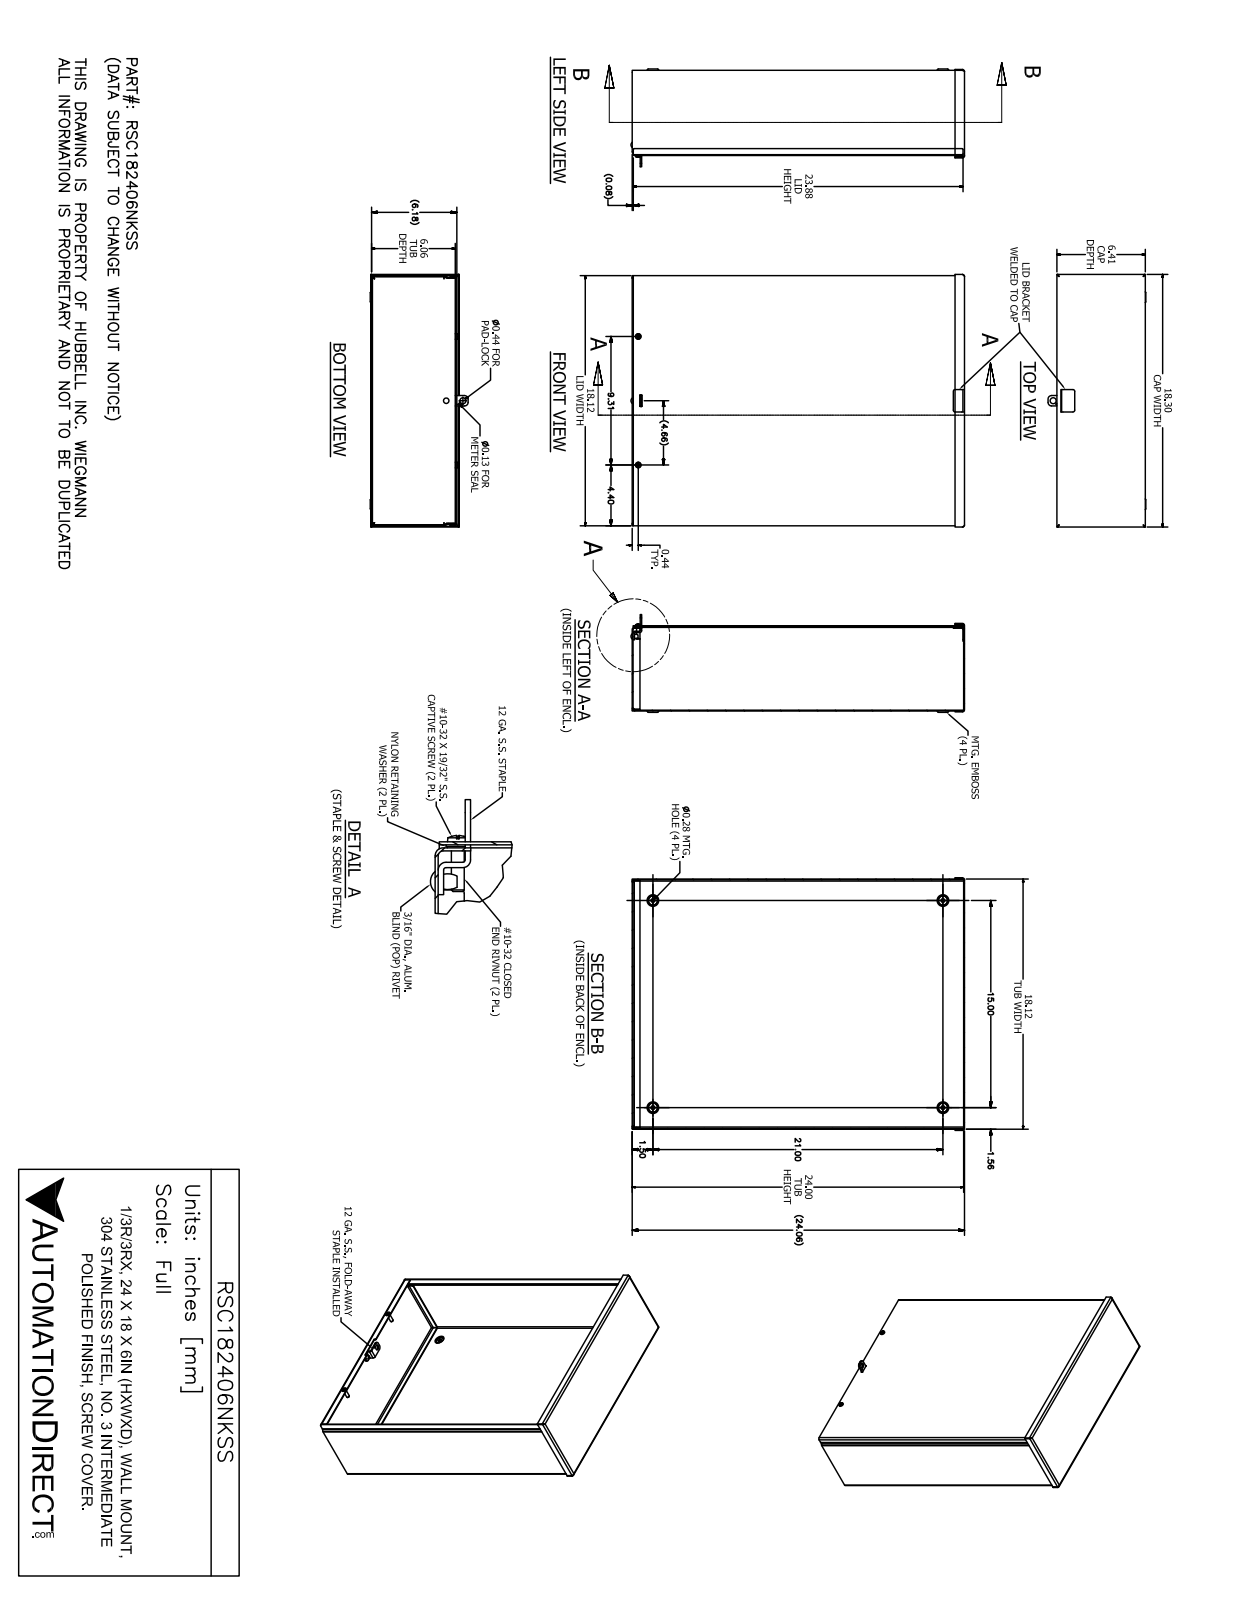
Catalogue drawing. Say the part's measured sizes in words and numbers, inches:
The part is named "RSC182406NKSS". Its 3-D file was written by "SolidWorks 2017 (AUTOMOTIVE_DESIGN)". It is 13 solids with 383 faces: 199 planar, 99 cylindrical and 85 other. Overall it measures 24.149 by 18.299 by 7.084 inches. Its volume is 85.89 cubic inches and its surface area 2 929 square inches. Round holes: 4 of diameter 0.25, 4 of diameter 0.281, 2 of diameter 0.156, 2 of diameter 0.196, 2 of diameter 0.257, 2 of diameter 0.278, 1 of diameter 0.125, 1 of diameter 0.198, 1 of diameter 0.201, 1 of diameter 0.437. Round bosses or shafts: 2 of diameter 0.453, 2 of diameter 0.406, 2 of diameter 0.248, 2 of diameter 0.167, 1 of diameter 0.187. Partial cylindrical surfaces (rounded edges, fillets, slot ends): 17 of radius 0.094, 17 of radius 0.153, 6 of radius 0.031, 4 of radius 0.125, 4 of radius 0.25, 2 of radius 0.047, 2 of radius 0.05, 2 of radius 0.062. The main face-to-face distances are 0.059, 6.117, 6.176, 6.058, 18.059, 24, 18.118, 18, 24.059, 23.941. The hole center spacings are 3.036, 3.047, 9.313, 12.203, 12.206, 15, 21, 22.245.
